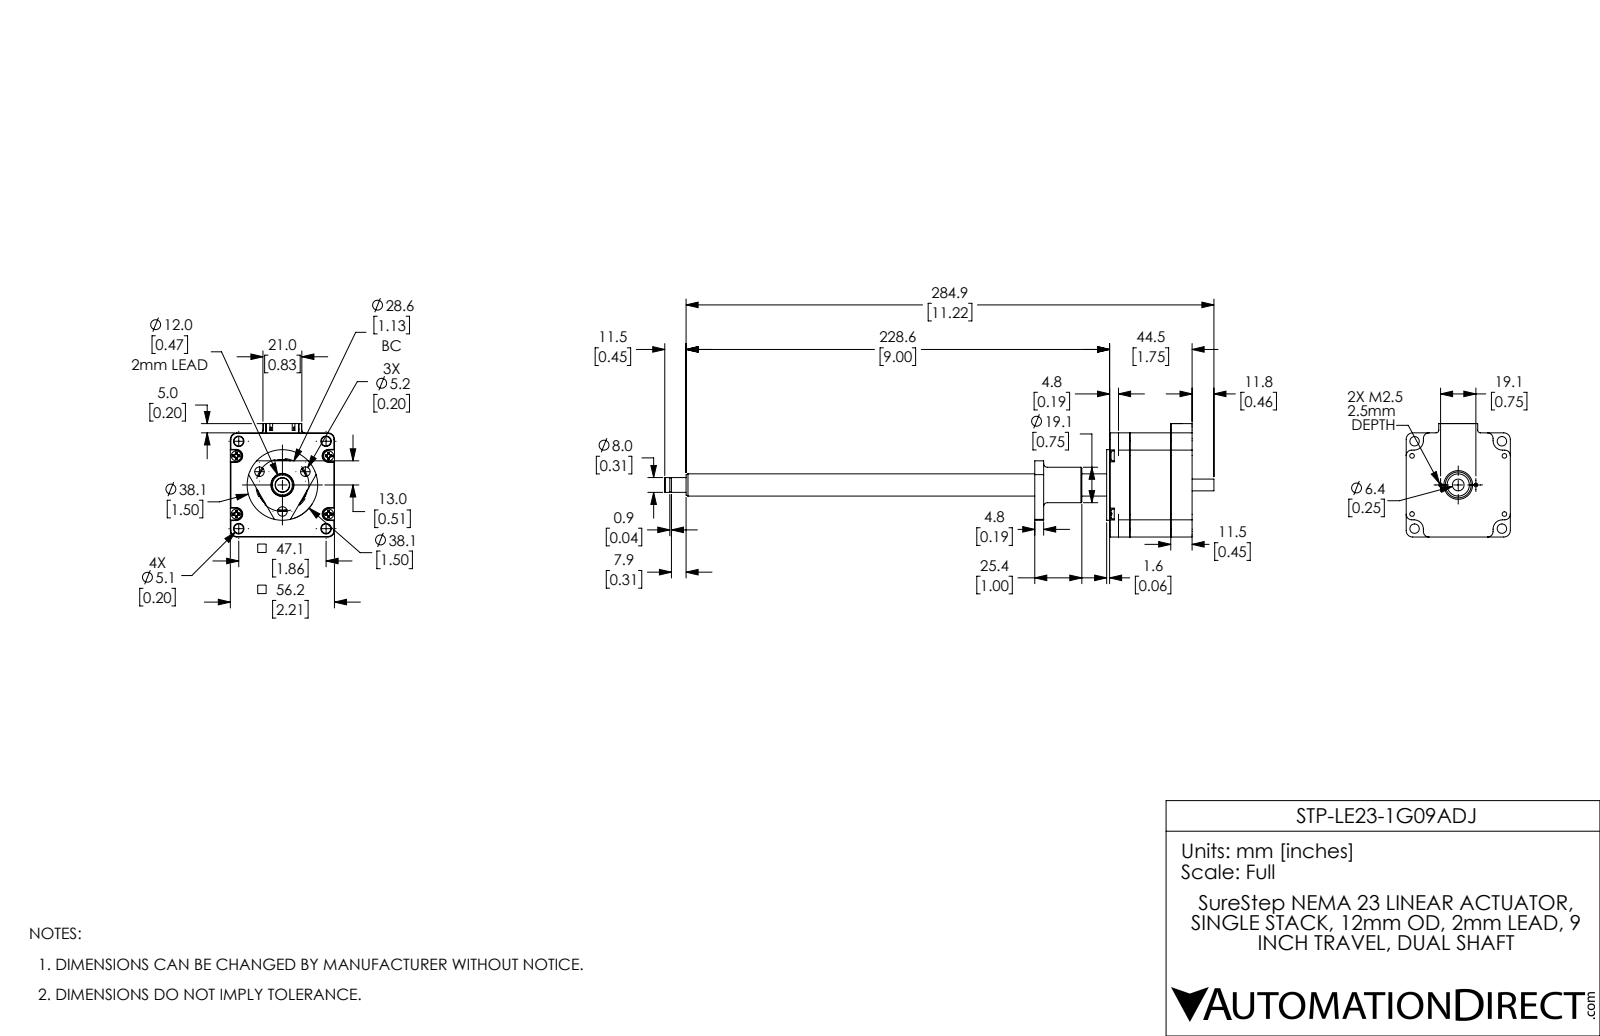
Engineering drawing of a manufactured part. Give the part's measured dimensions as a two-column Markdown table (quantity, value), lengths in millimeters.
| quantity | value |
| --- | --- |
| part name | STP-LE23-1G09ADJ_1; STP-LE23-1G09ADJ_2; STP-LE23-1G09ADJ |
| STEP written by | SolidWorks 2017 (AUTOMOTIVE_DESIGN) |
| units | millimeters |
| bodies | 8 solids, 751 faces (306 planar, 205 cylindrical, 240 other) |
| overall size | 296.4 × 61.22 × 56.2 |
| volume | 133 794 mm³ |
| surface area | 53 571 mm² |
| round holes (diameter × count) | 4.5 × 8, 2.5 × 4, 3.3 × 4, 5.1 × 4, 5.16 × 3, 2 × 2, 2.05 × 2, 6.8 × 1, 10.5 × 1, 15.5 × 1, 20 × 1, 24 × 1 |
| round bosses / shafts (diameter × count) | 5.4 × 4, 38.1 × 1, 36 × 1, 35.6 × 1, 34.85 × 1, 19.1 × 1, 16 × 1, 12 × 1 |
| partial cylindrical surfaces (radius × count) | 1.5 × 10, 3 × 8, 1.8 × 4, 3.2 × 4, 3.5 × 4, 5 × 4, 19.3 × 1 |
| main face-to-face distances | 22, 44.5, 56.2, 11.5, 33.5, 1.6, 51.4, 11, 33, 38.8 |
| hole center spacings | 14.12, 24.75, 33.05, 35.01, 45.74, 48.53, 56.99, 6.55 |
